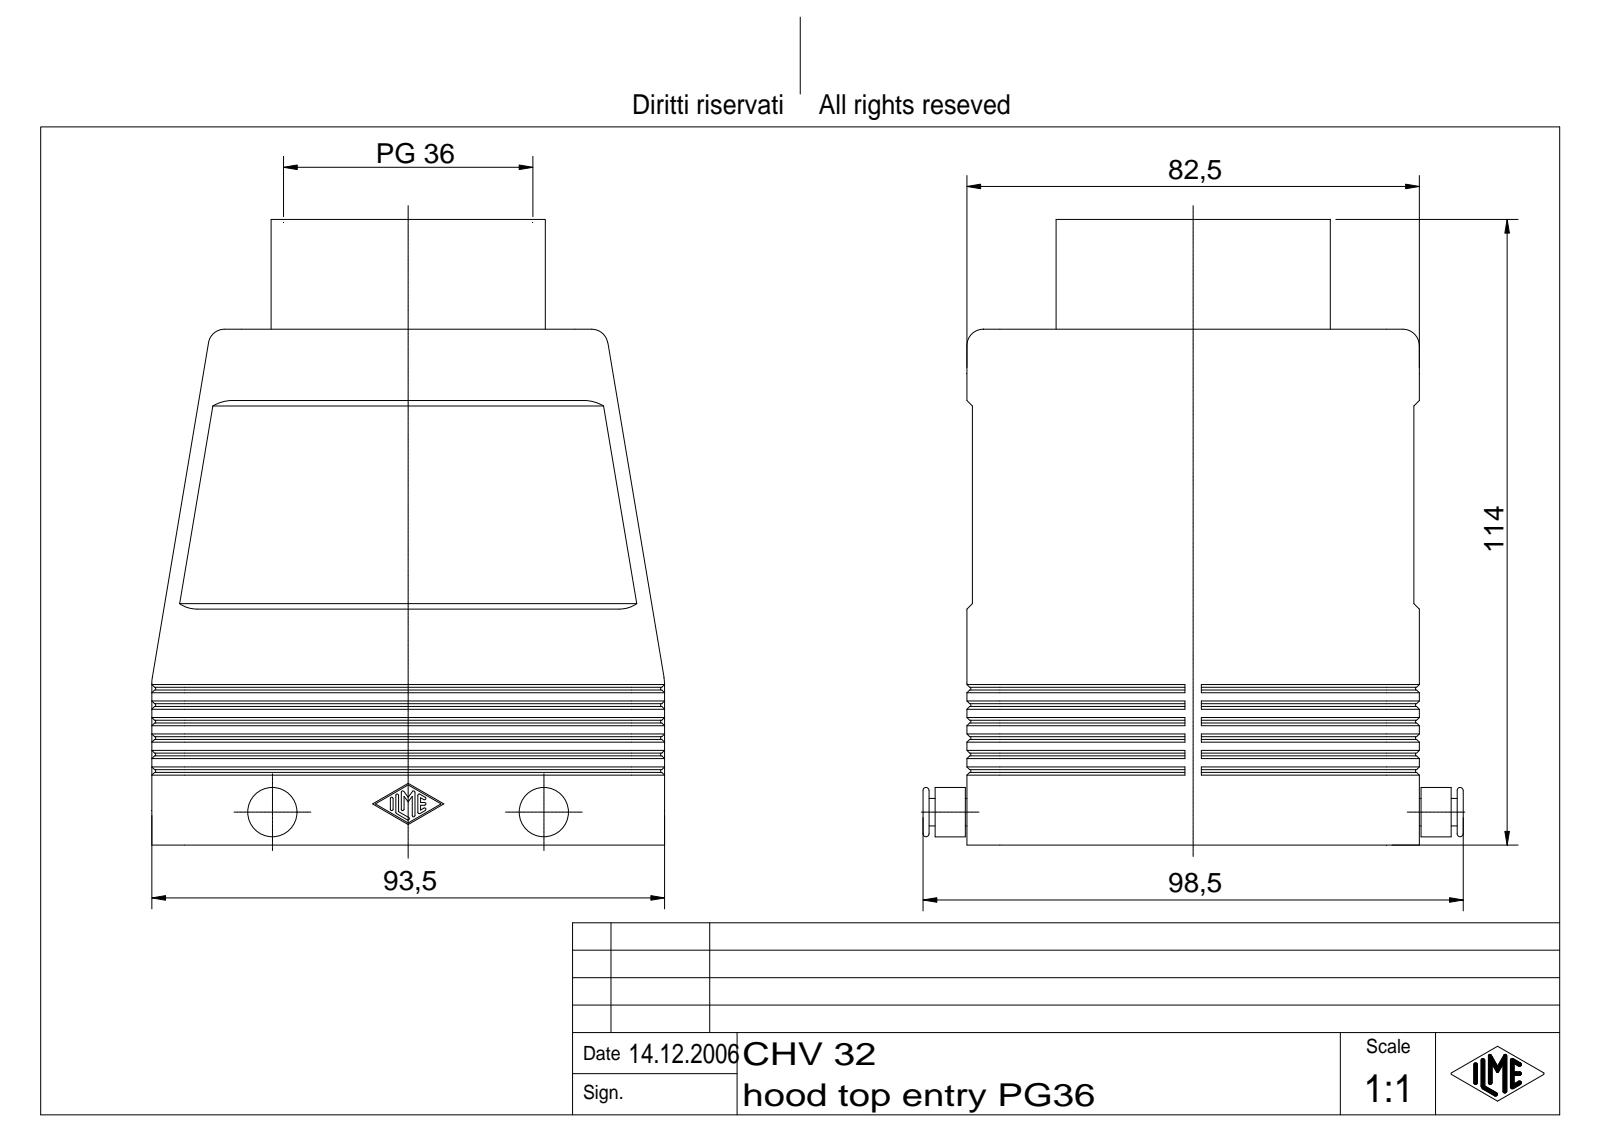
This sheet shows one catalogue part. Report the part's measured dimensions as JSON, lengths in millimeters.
{"part_name": "CHV 32", "step_written_by": "Autodesk Inventor 7 (AUTOMOTIVE_DESIGN)", "units": "millimeters", "bodies": {"solids": 1, "faces": 620, "planar": 210, "cylindrical": 162, "other": 248}, "overall_size": [114, 98.5, 93.5], "volume_mm3": 155363, "surface_area_mm2": 80995, "round_holes": [[2.46, 4], [3.5, 4], [43.48, 1], [45.48, 1], [51, 1]], "round_bosses_or_shafts": [[9, 2], [5, 2], [65, 1], [50, 1]], "partial_cylinders_radius": [[0.25, 14], [2, 12], [6, 10], [3, 4], [5.3, 2]], "face_to_face_distances": [4, 78.5, 74.5, 82.5, 3, 1, 71.5, 11, 77.5, 81.5], "hole_center_spacings": [27, 38.96, 49.62, 77.5, 82.07]}
